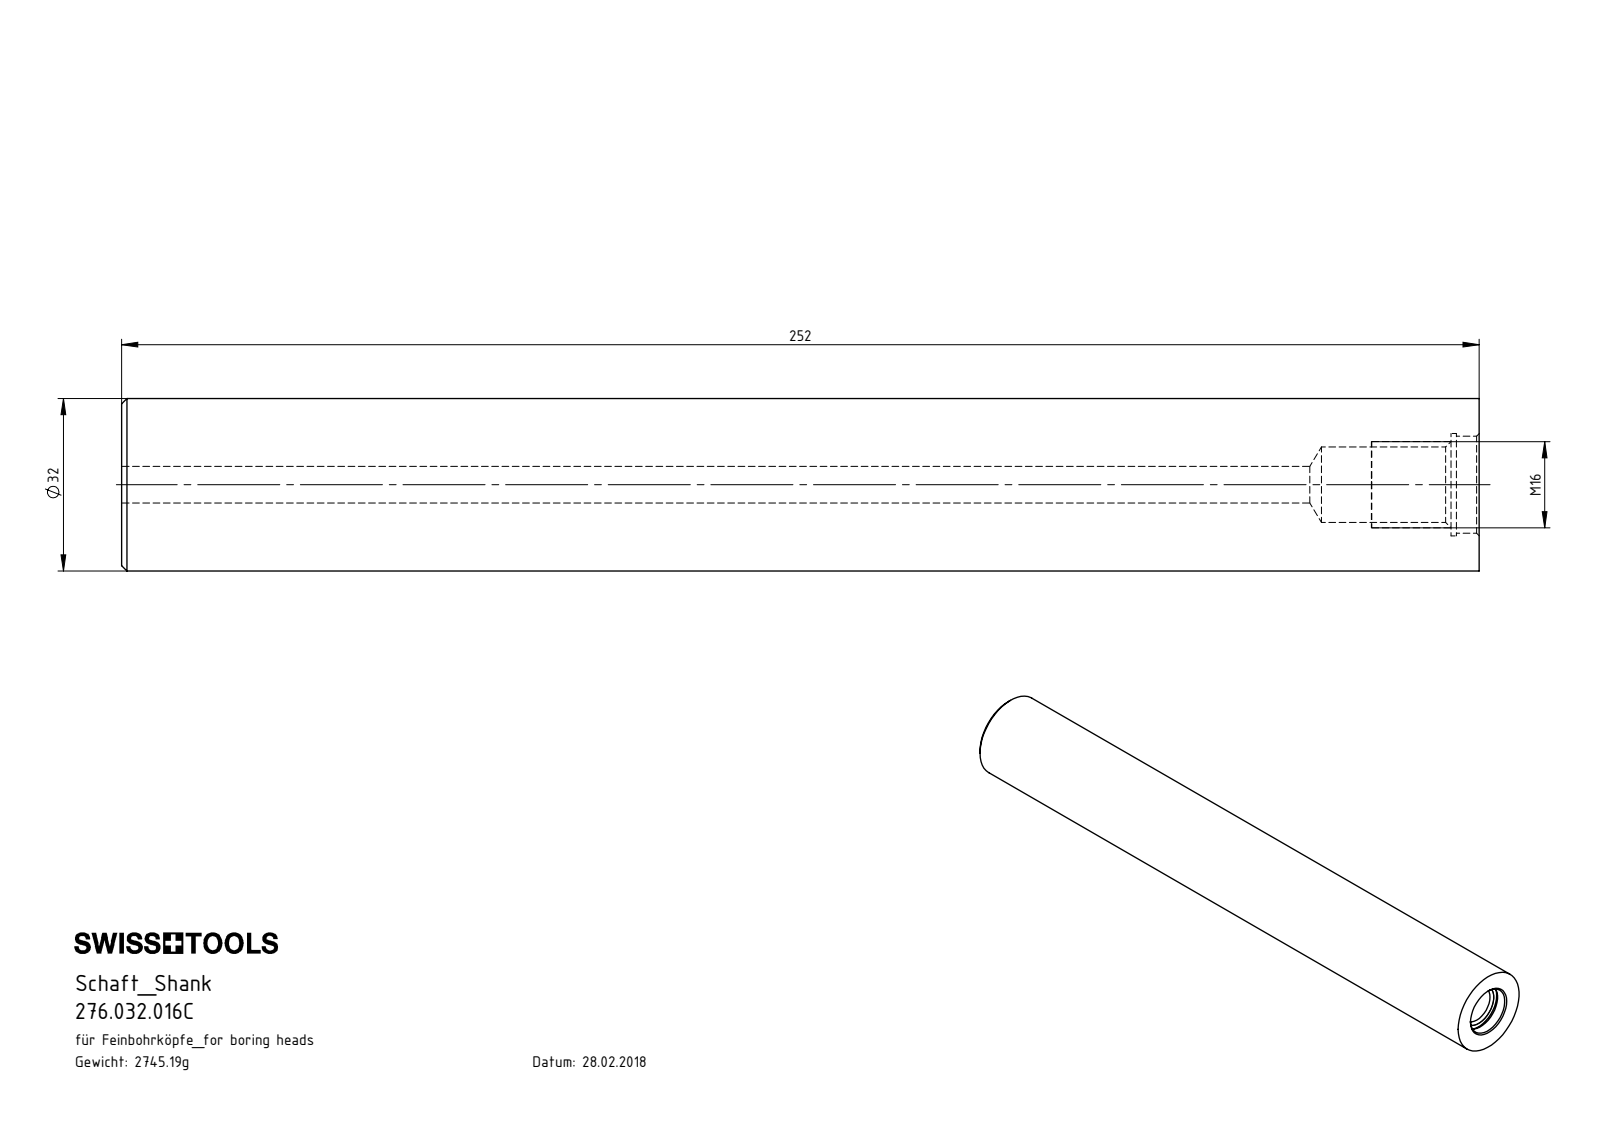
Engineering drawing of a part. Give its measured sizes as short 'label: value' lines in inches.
name: 276.032.016C
written by: SolidWorks 2017 (CONFIG_CONTROL_DESIGN)
unit: in
bodies: 1 solid, 22 faces (4 planar, 10 cylindrical, 8 other)
size: 9.921 × 1.26 × 1.26
volume: 11.55 in³; area: 51.02 in²
holes: 1× ⌀0.268, 1× ⌀0.551, 1× ⌀0.709, 1× ⌀0.748
bosses: 1× ⌀1.26
face distances: 9.921, 9.715, 0.207, 9.754, 0.039, 0.167
